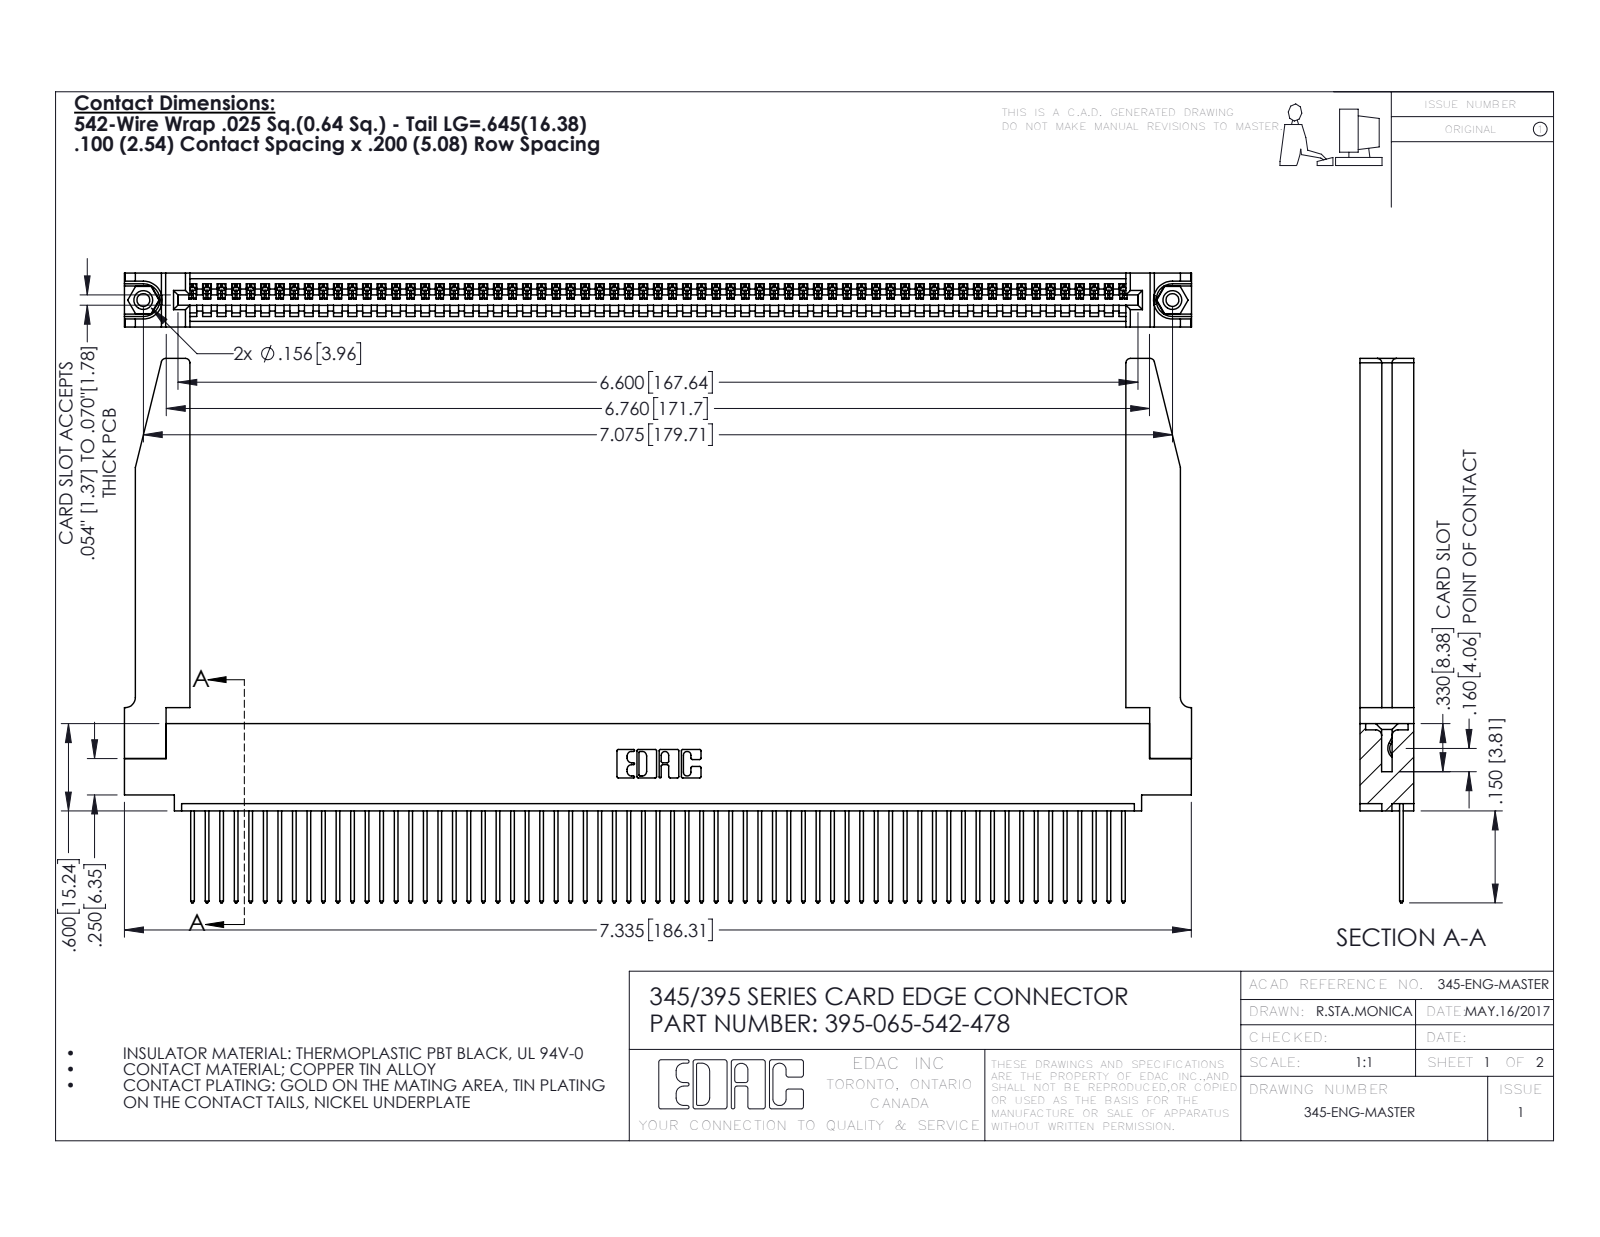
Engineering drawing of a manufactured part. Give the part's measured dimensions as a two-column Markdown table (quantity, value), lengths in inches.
| quantity | value |
| --- | --- |
| part name | 345-292-001_345-293-142; 345-220-078_345-220-078; 395-065-542-478; 345-250-001_345-250-001-102 (+1 more) |
| STEP written by | SolidWorks 2016 (CONFIG_CONTROL_DESIGN) |
| units | inches |
| bodies | 70 solids, 4134 faces (2826 planar, 1256 cylindrical, 52 other) |
| overall size | 7.336 × 3.742 × 0.37 |
| volume | 1.57 in³ |
| surface area | 49.63 in² |
| round holes (diameter × count) | 0.089 × 2, 0.125 × 2, 0.156 × 2, 0.064 × 1 |
| round bosses / shafts (diameter × count) | 0.155 × 2 |
| partial cylindrical surfaces (radius × count) | 0.006 × 130, 0.01 × 130, 0.01 × 22, 0.03 × 8, 0.007 × 6, 0.031 × 6, 0.026 × 3, 0.031 × 2 |
| main face-to-face distances | 0.072, 0.298, 0.37, 0.098, 0.272, 0.025, 0.2, 0.225, 0.148, 0.15 |
| hole center spacings | 0.27, 6.839, 7.075 |
